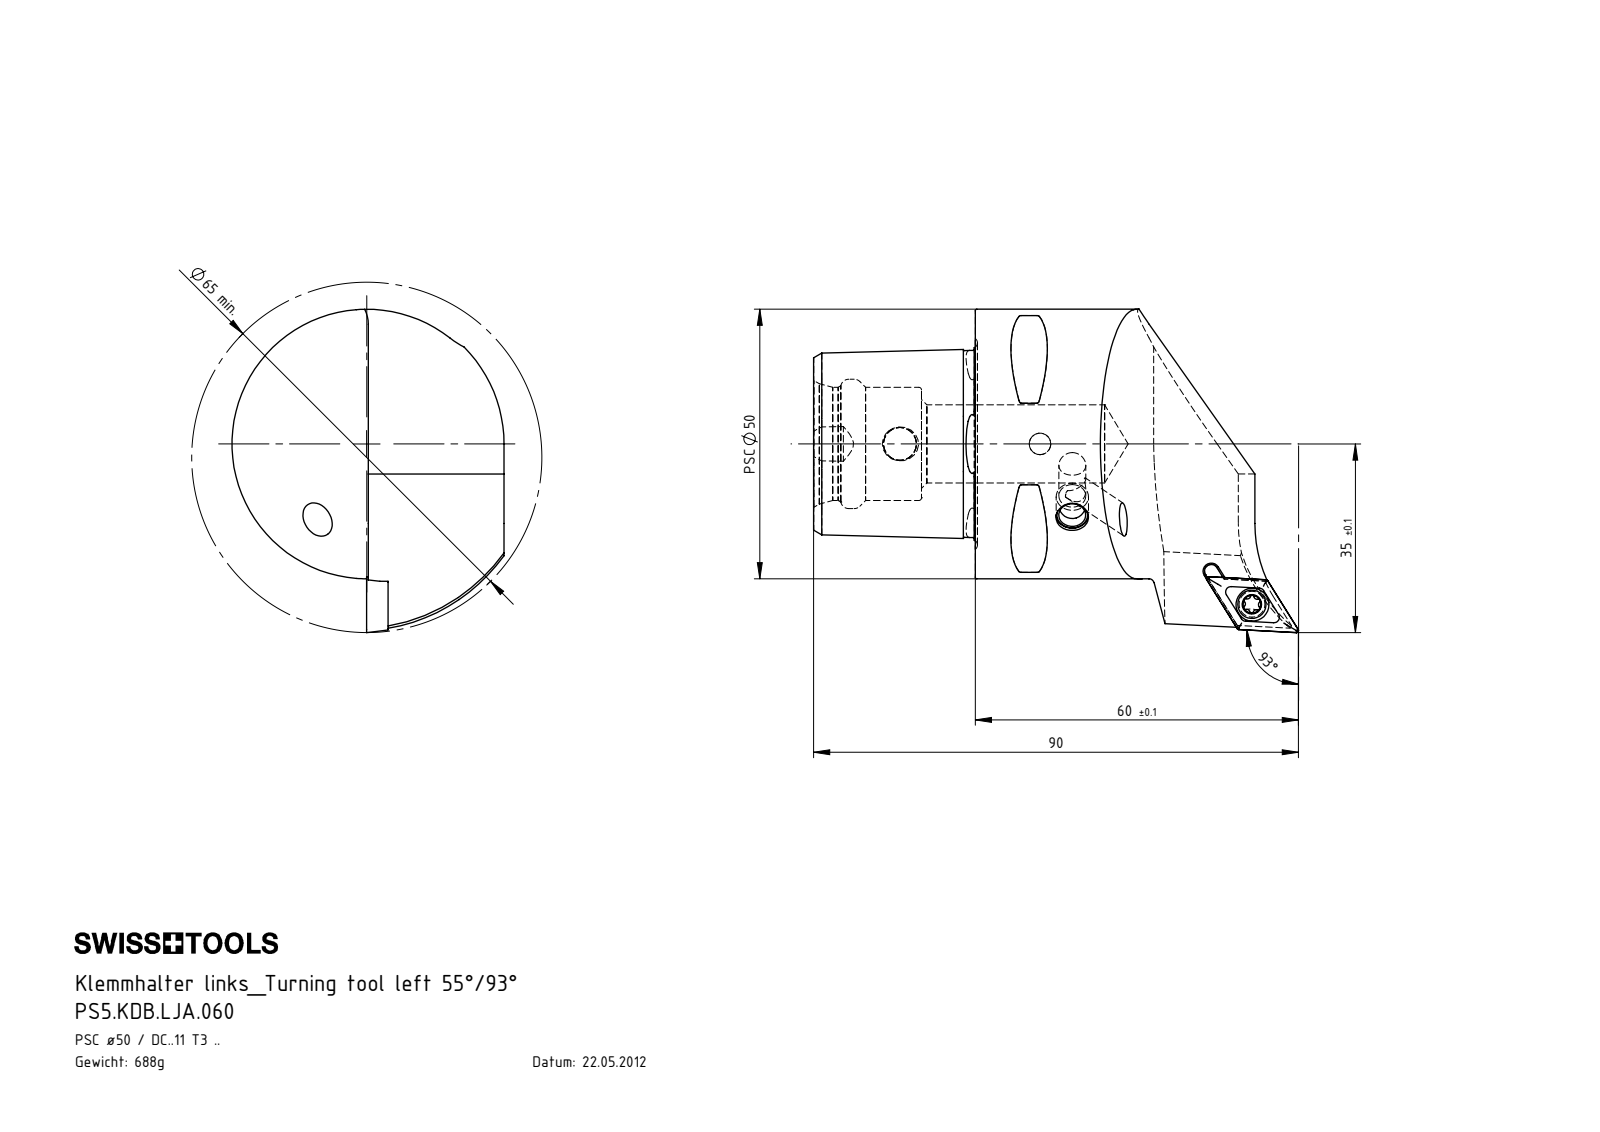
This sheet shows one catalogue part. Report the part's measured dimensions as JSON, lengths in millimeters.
{"part_name": "PS5-KDB.LJA.060; KVT_MB_600_060; DCMT11T304; WCB-ER2.001.009_A (+1 more)", "step_written_by": "SolidWorks 2012 (CONFIG_CONTROL_DESIGN)", "units": "millimeters", "bodies": {"solids": 5, "faces": 269, "planar": 51, "cylindrical": 68, "other": 150}, "overall_size": [90.01, 60, 50.5], "volume_mm3": 87447, "surface_area_mm2": 18908, "round_holes": [[5, 3], [6.1, 2], [3.3, 1], [4, 1], [4.4, 1], [6, 1], [14.5, 1], [21, 1], [24, 1]], "round_bosses_or_shafts": [[50, 1], [6, 1], [5.25, 1], [4, 1]], "partial_cylinders_radius": [[0.5, 8], [0.34, 6], [0.59, 6], [1.25, 1], [3, 1], [4, 1], [25.5, 1], [26, 1]], "face_to_face_distances": [30, 25.2, 19.18, 21.53, 3.67, 44.4, 20, 10, 29.8, 9.8], "hole_center_spacings": [26, 49.32, 49.45, 71.8, 71.92]}
